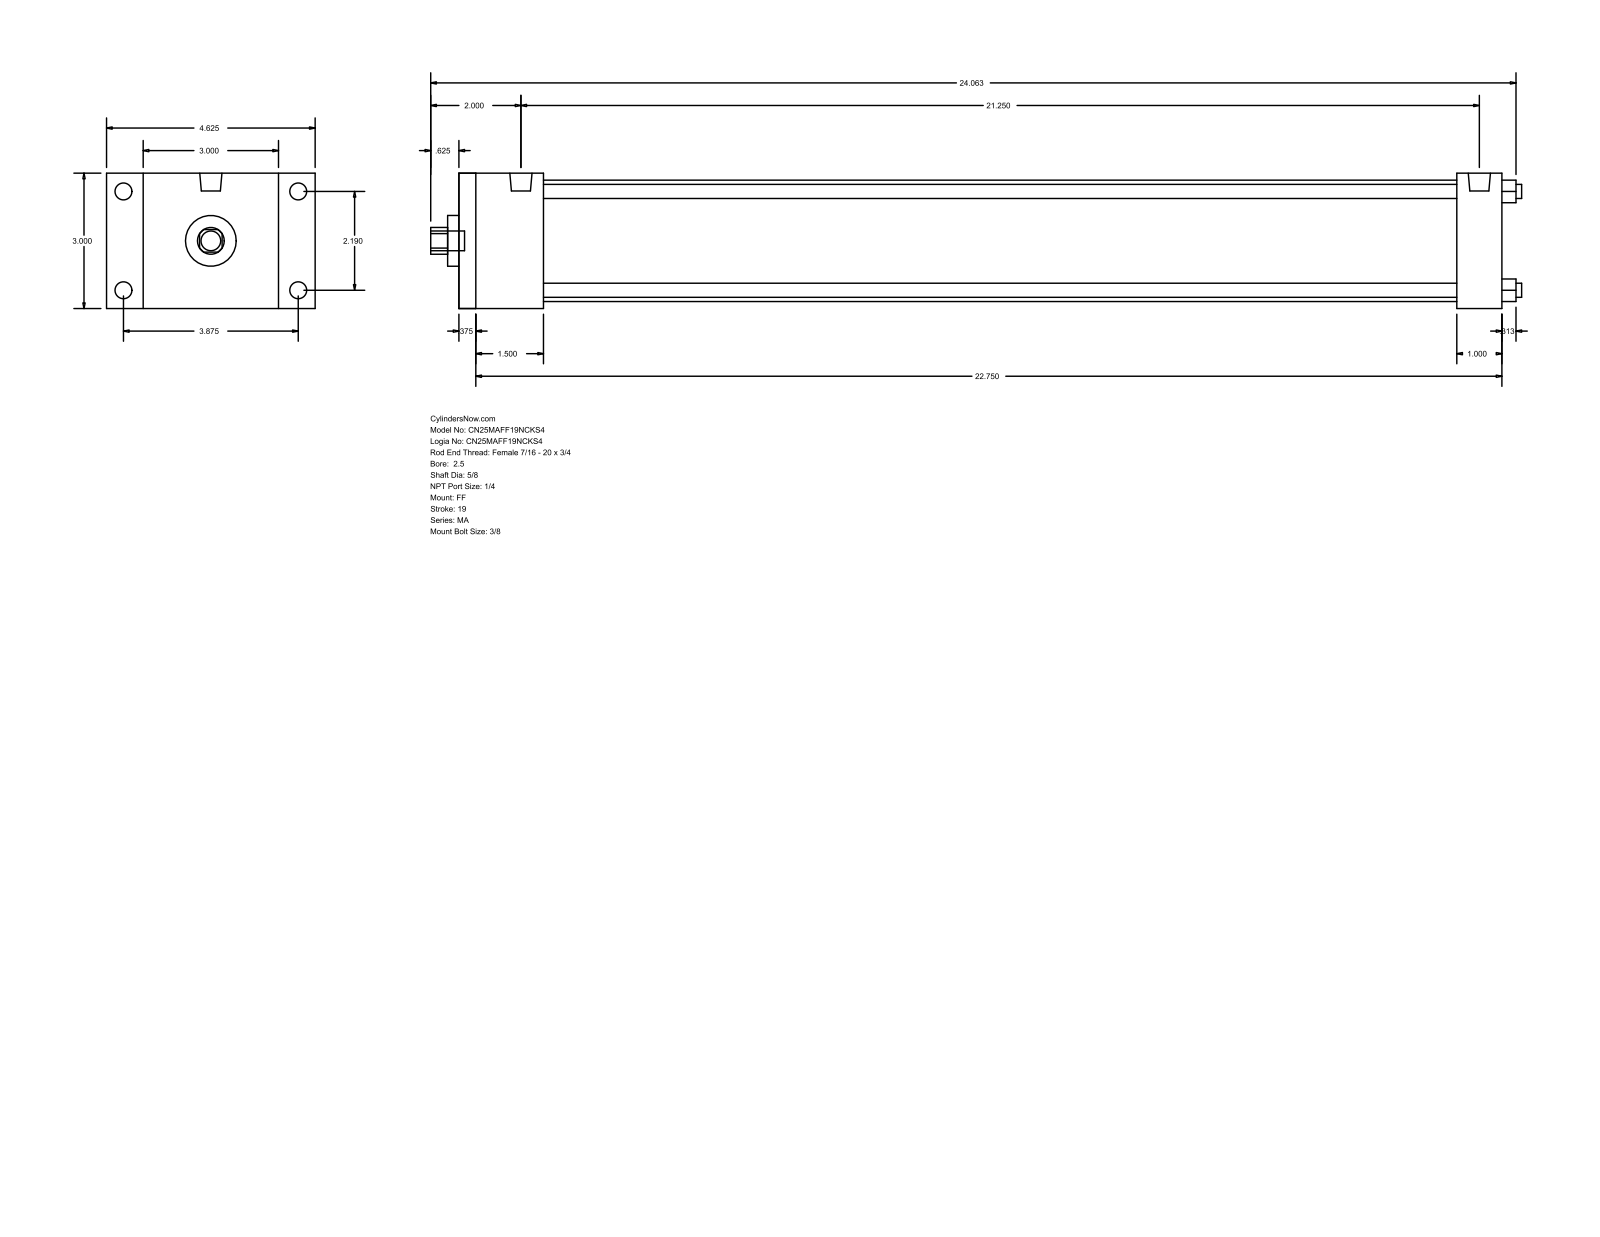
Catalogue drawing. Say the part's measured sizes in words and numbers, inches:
The part is named "MA_FF__0250_0.625". Its 3-D file was written by "GSSL Pune (CONFIG_CONTROL_DESIGN)". It is 0 solids with 92 faces: 64 planar, 28 cylindrical and 0 other. Overall it measures 24.187 by 4.625 by 3 inches. Round holes: 4 of diameter 0.313, 1 of diameter 0.625, 1 of diameter 1.125, 1 of diameter 2.69. Round bosses or shafts: 4 of diameter 0.375, 4 of diameter 0.313, 2 of diameter 0.492, 1 of diameter 0.437. Partial cylindrical surfaces (rounded edges, fillets, slot ends): 1 of radius 0.297. The main face-to-face distances are 3, 23.125, 0.375, 22.75, 1, 1.875, 22.125, 1.5, 21.75, 20.25. The hole center spacings are 1.548, 2.19, 3.097.
